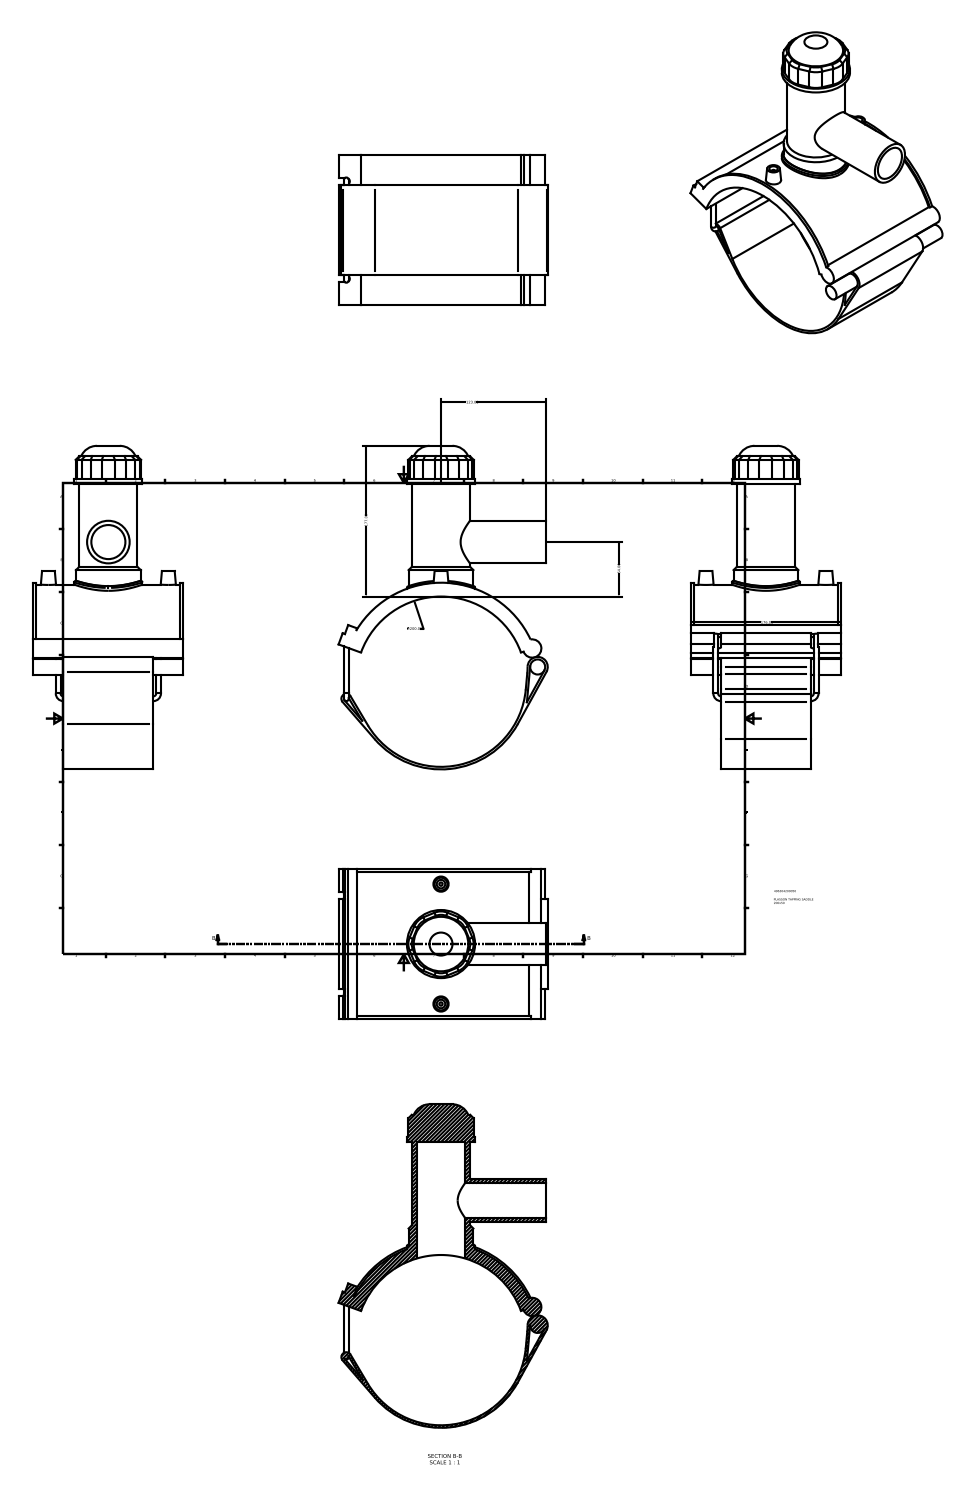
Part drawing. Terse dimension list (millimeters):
name: 496304200050
written by: Autodesk Inventor 2015 (AUTOMOTIVE_DESIGN)
unit: mm
bodies: 1 solid, 121 faces (68 planar, 38 cylindrical, 15 other)
size: 380 × 245.66 × 176
volume: 1 312 000 mm³; area: 313 415 mm²
holes: 2× ⌀10, 1× ⌀40, 1× ⌀56
bosses: 2× ⌀5.6, 2× ⌀4, 1× ⌀80, 1× ⌀76, 1× ⌀68, 1× ⌀50, 1× ⌀17.69
rounds: 8× R20, 2× R4.2, 2× R100, 1× R2.8, 1× R5.8, 1× R10.77, 1× R11.85, 1× R103
face distances: 3, 176, 3.02, 35.2, 140.8, 11.2, 14, 2.68, 25.21, 2.8
hole spacings: 70.4, 140.8
